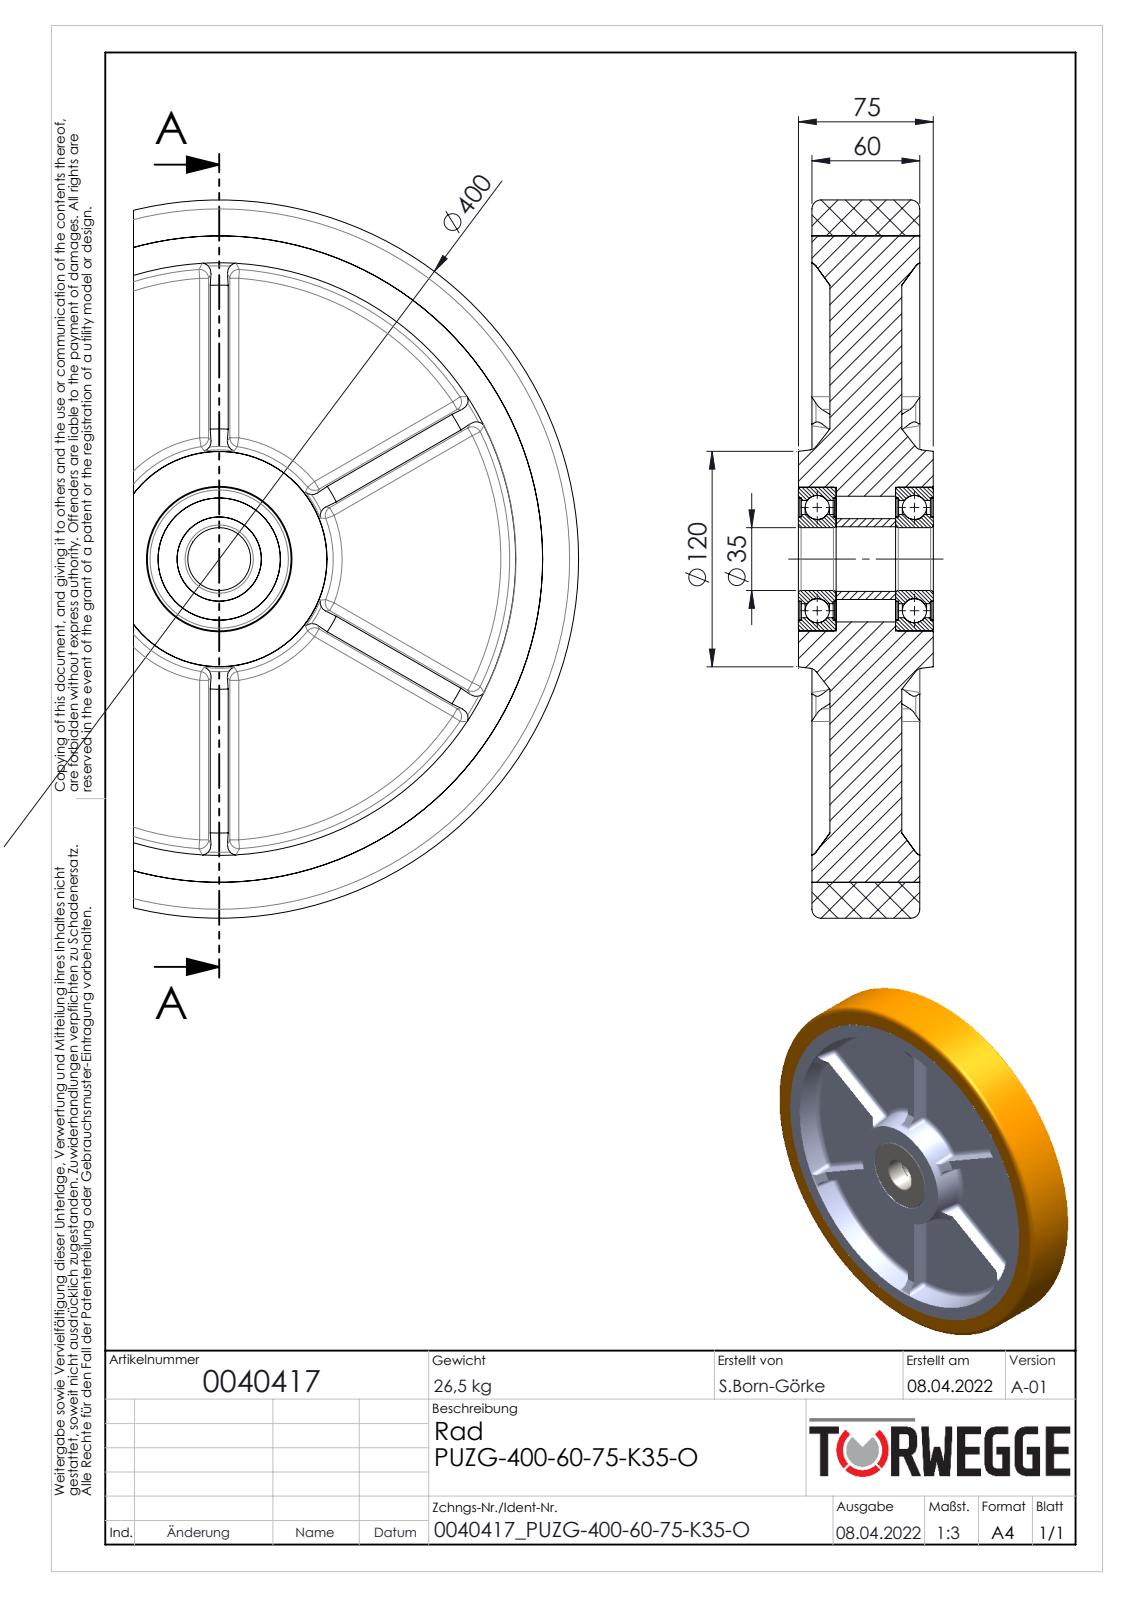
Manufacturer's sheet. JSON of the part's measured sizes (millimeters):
{"part_name": "0040417", "step_written_by": "SolidWorks 2020 (AUTOMOTIVE_DESIGN)", "units": "millimeters", "bodies": {"solids": 13, "faces": 439, "planar": 82, "cylindrical": 96, "other": 261}, "overall_size": [400, 400, 75.1], "volume_mm3": 4205000, "surface_area_mm2": 635873, "round_holes": [[35, 1], [36, 1], [46.93, 1], [65.33, 1], [68.08, 1], [70, 1], [80, 1], [360, 1]], "round_bosses_or_shafts": [[400, 1], [49.67, 1], [45, 1]], "partial_cylinders_radius": [[5, 16]], "face_to_face_distances": [25, 35, 10, 60, 7.5, 32.5, 42.5, 67.5, 13.44, 54.05]}
